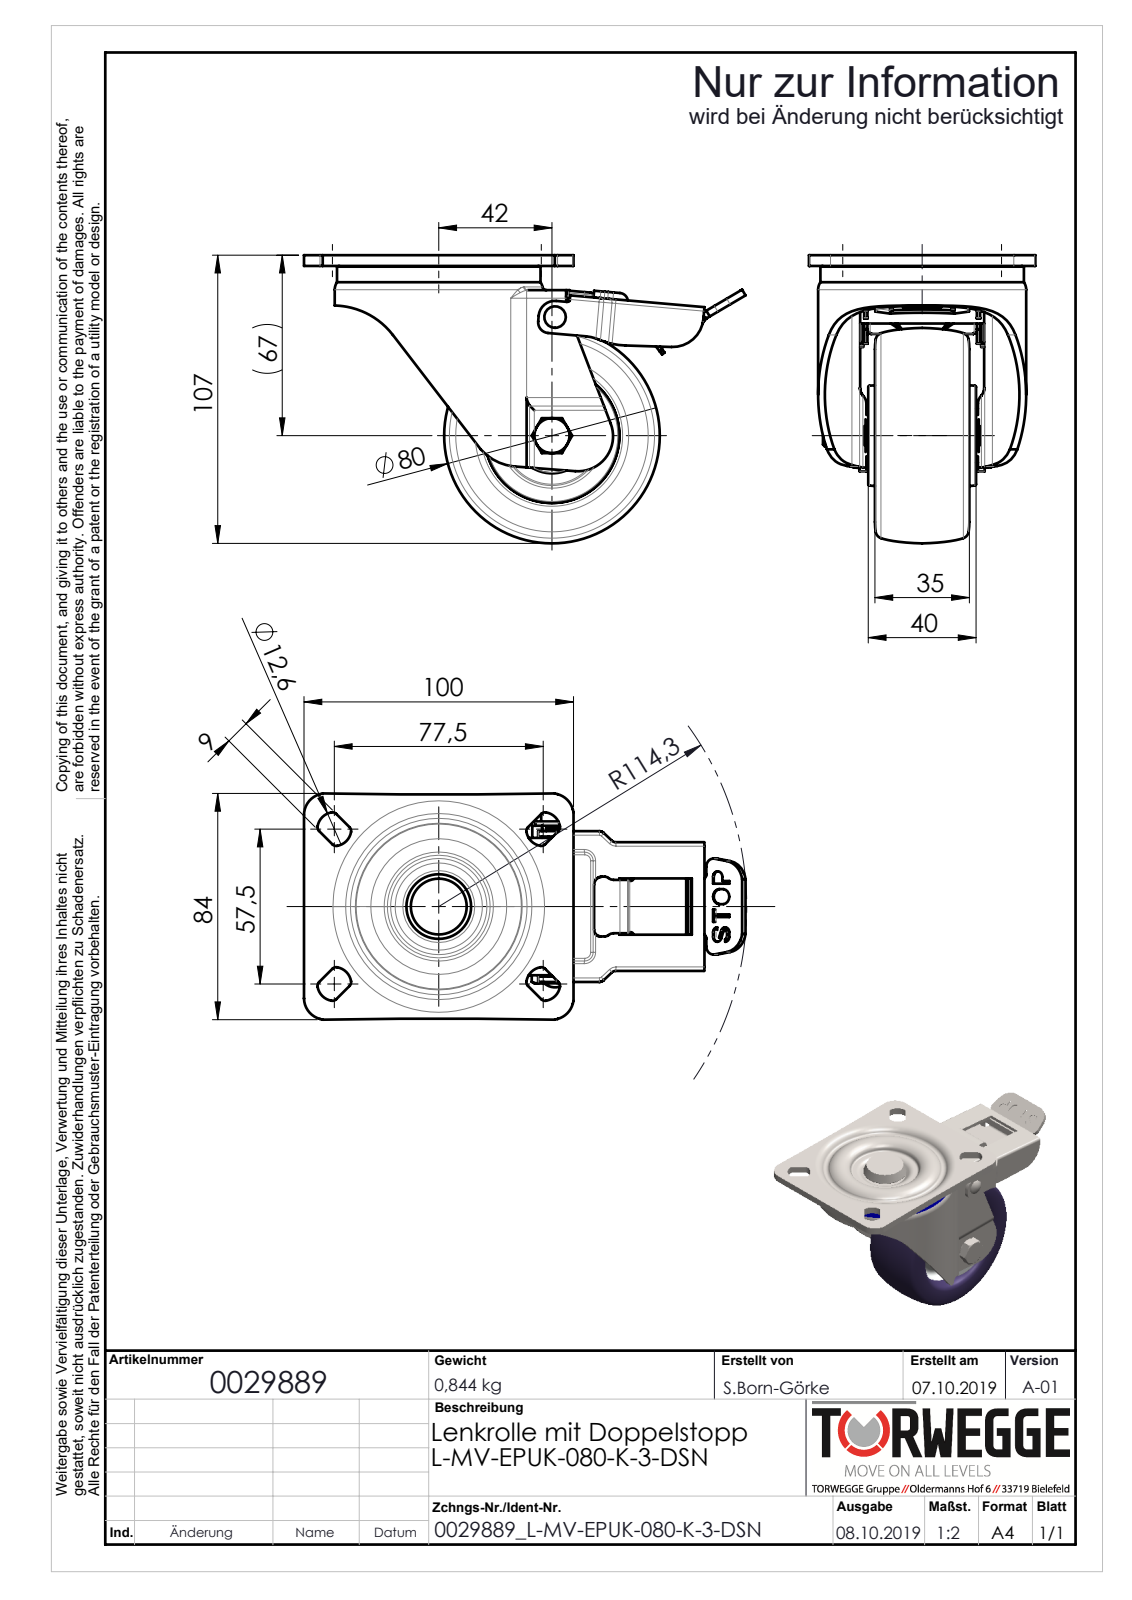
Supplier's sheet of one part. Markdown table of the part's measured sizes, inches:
| quantity | value |
| --- | --- |
| part name | 0029889_L-MV-EPUK-080-K-3-DSN_(A-01) |
| STEP written by | SolidWorks 2018 (AUTOMOTIVE_DESIGN) |
| units | inches |
| bodies | 20 solids, 1030 faces (318 planar, 331 cylindrical, 381 other) |
| overall size | 6.45 × 4.213 × 3.307 |
| volume | 16.49 in³ |
| surface area | 191.6 in² |
| round holes (diameter × count) | 0.197 × 2, 0.118 × 1, 0.205 × 1, 0.262 × 1, 0.323 × 1, 0.335 × 1, 0.472 × 1, 0.488 × 1, 0.661 × 1, 0.906 × 1, 0.913 × 1, 1.102 × 1 |
| round bosses / shafts (diameter × count) | 0.512 × 2, 0.315 × 2, 3.039 × 1, 2.972 × 1, 0.945 × 1, 0.787 × 1, 0.591 × 1, 0.48 × 1 |
| partial cylindrical surfaces (radius × count) | 0.079 × 39, 0.039 × 23, 0.157 × 17, 0.049 × 10, 0.059 × 8, 0.118 × 8, 0.315 × 6, 0.098 × 5 |
| main face-to-face distances | 0.098, 0.157, 0.079, 0.531, 0.047, 0.028, 1.819, 0.689, 0.091, 0.126 |
| hole center spacings | 1.734 |
